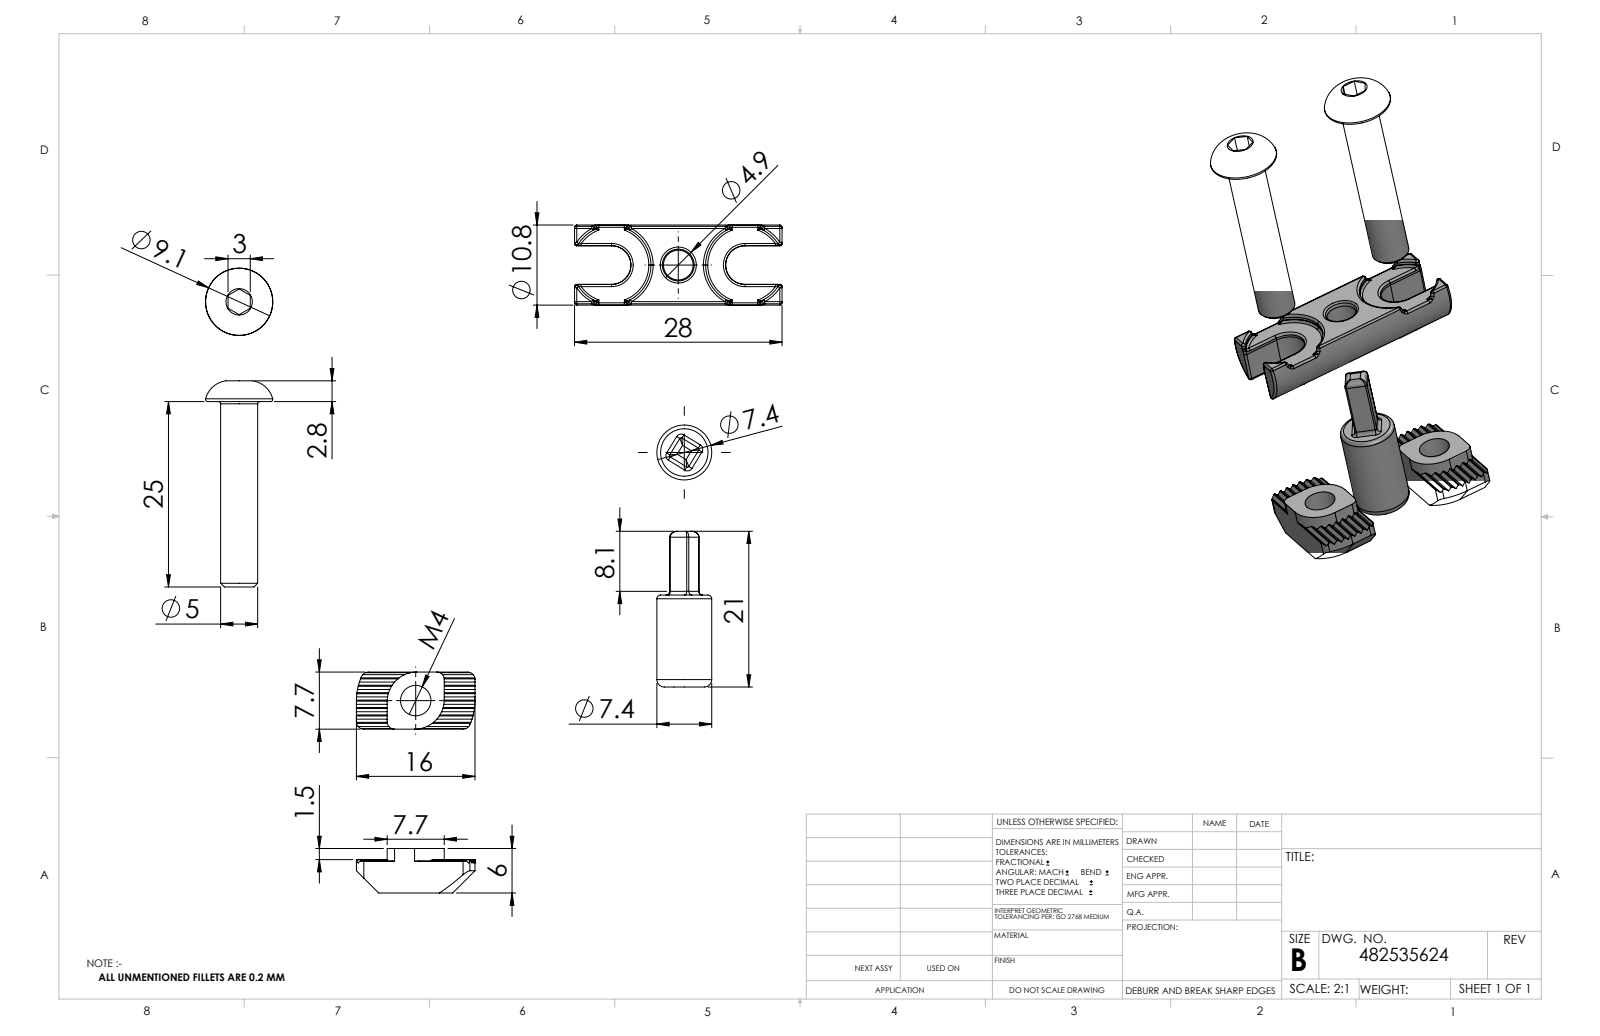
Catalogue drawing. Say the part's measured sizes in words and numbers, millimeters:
The part is named "482535624_Bolzenverbinder_30_NUt8". Its 3-D file was written by "Autodesk Inventor 2019 (AUTOMOTIVE_DESIGN)". It is 6 solids with 387 faces: 130 planar, 113 cylindrical and 144 other. Overall it measures 33.68 by 28 by 16 millimeters. Its volume is 3 763 cubic millimeters and its surface area 3 612 square millimeters. Round holes: 2 of diameter 4.1, 1 of diameter 4. Round bosses or shafts: 2 of diameter 5, 1 of diameter 7.4. Partial cylindrical surfaces (rounded edges, fillets, slot ends): 22 of radius 0.3, 14 of radius 0.1, 12 of radius 1, 4 of radius 0.2, 4 of radius 0.5, 4 of radius 0.8, 4 of radius 4, 2 of radius 8. The main face-to-face distances are 18, 7.7, 23, 0.71, 2.12, 1.41, 6, 17, 24, 1. The hole center spacings are 9, 18.
